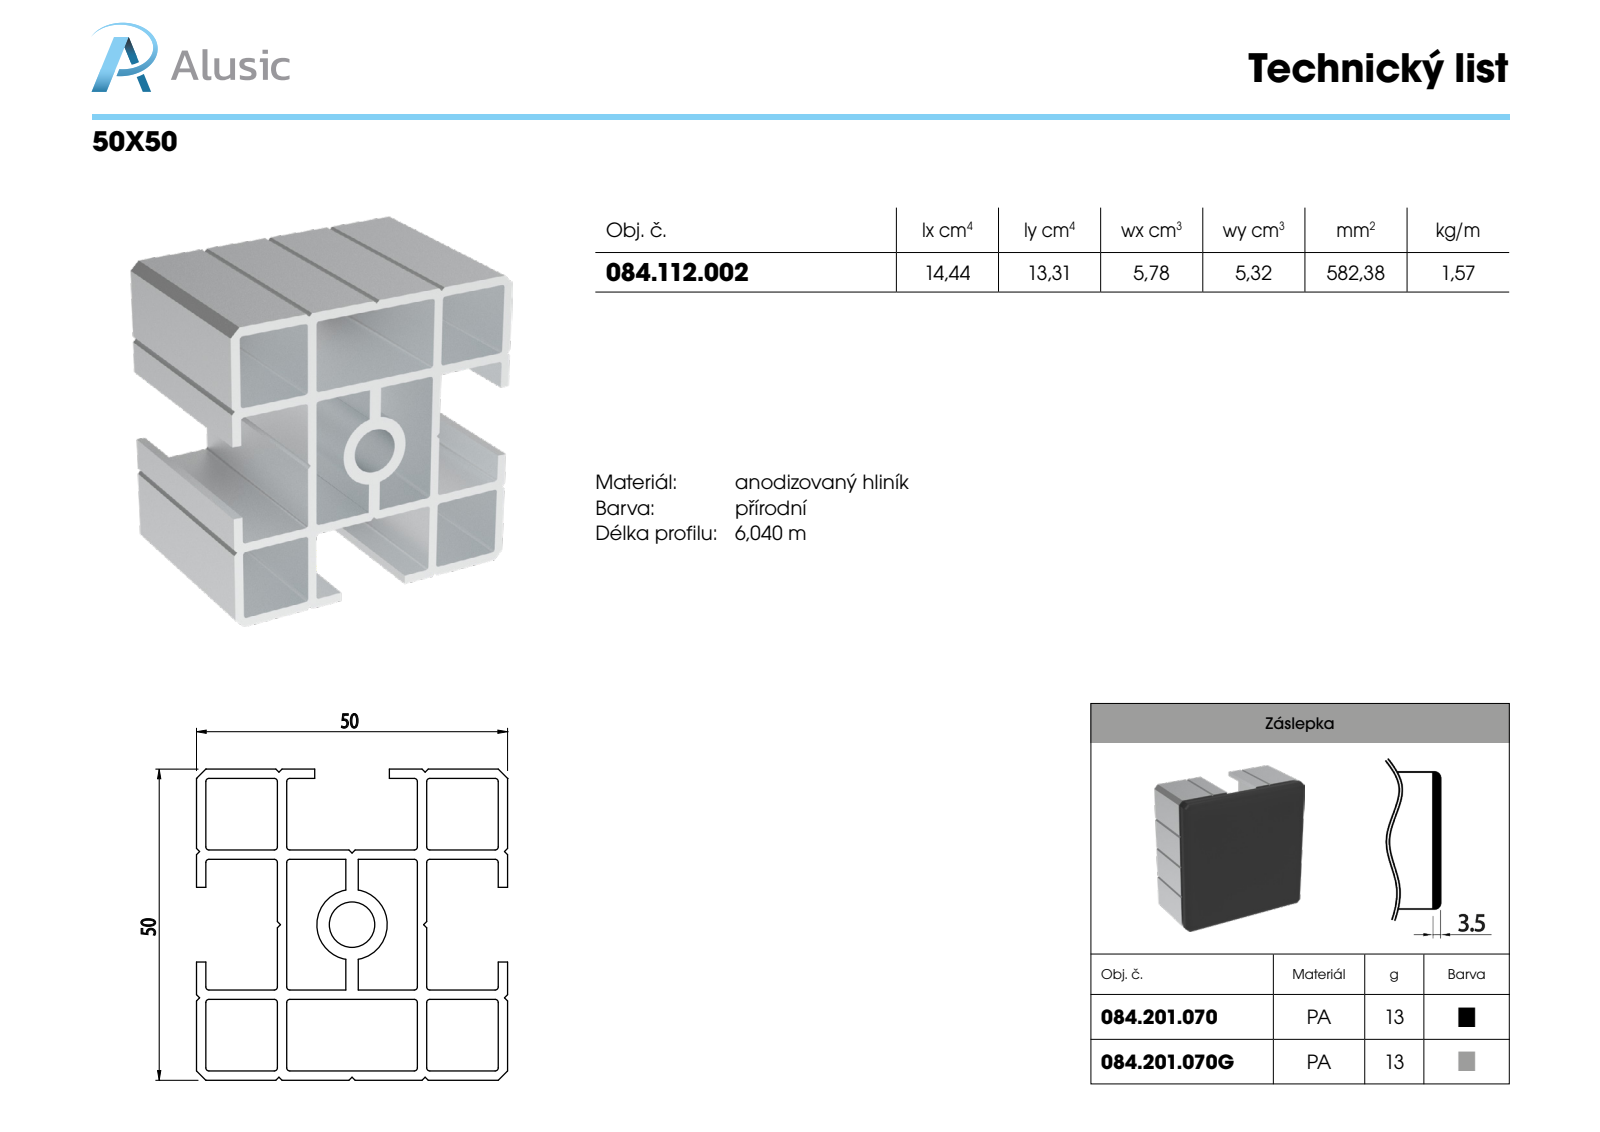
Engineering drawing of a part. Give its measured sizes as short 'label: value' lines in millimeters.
name: 084.112.002
written by: SolidWorks 2018 (AUTOMOTIVE_DESIGN)
unit: mm
bodies: 1 solid, 140 faces (100 planar, 40 cylindrical, 0 other)
size: 100 × 50 × 50
volume: 58 238 mm³; area: 74 055 mm²
holes: 1× ⌀7.3
bosses: 1× ⌀11.3
rounds: 36× R0.5
face distances: 1.5, 13, 35.5, 22.5, 11.5, 37, 14.5, 34, 48.5, 24
